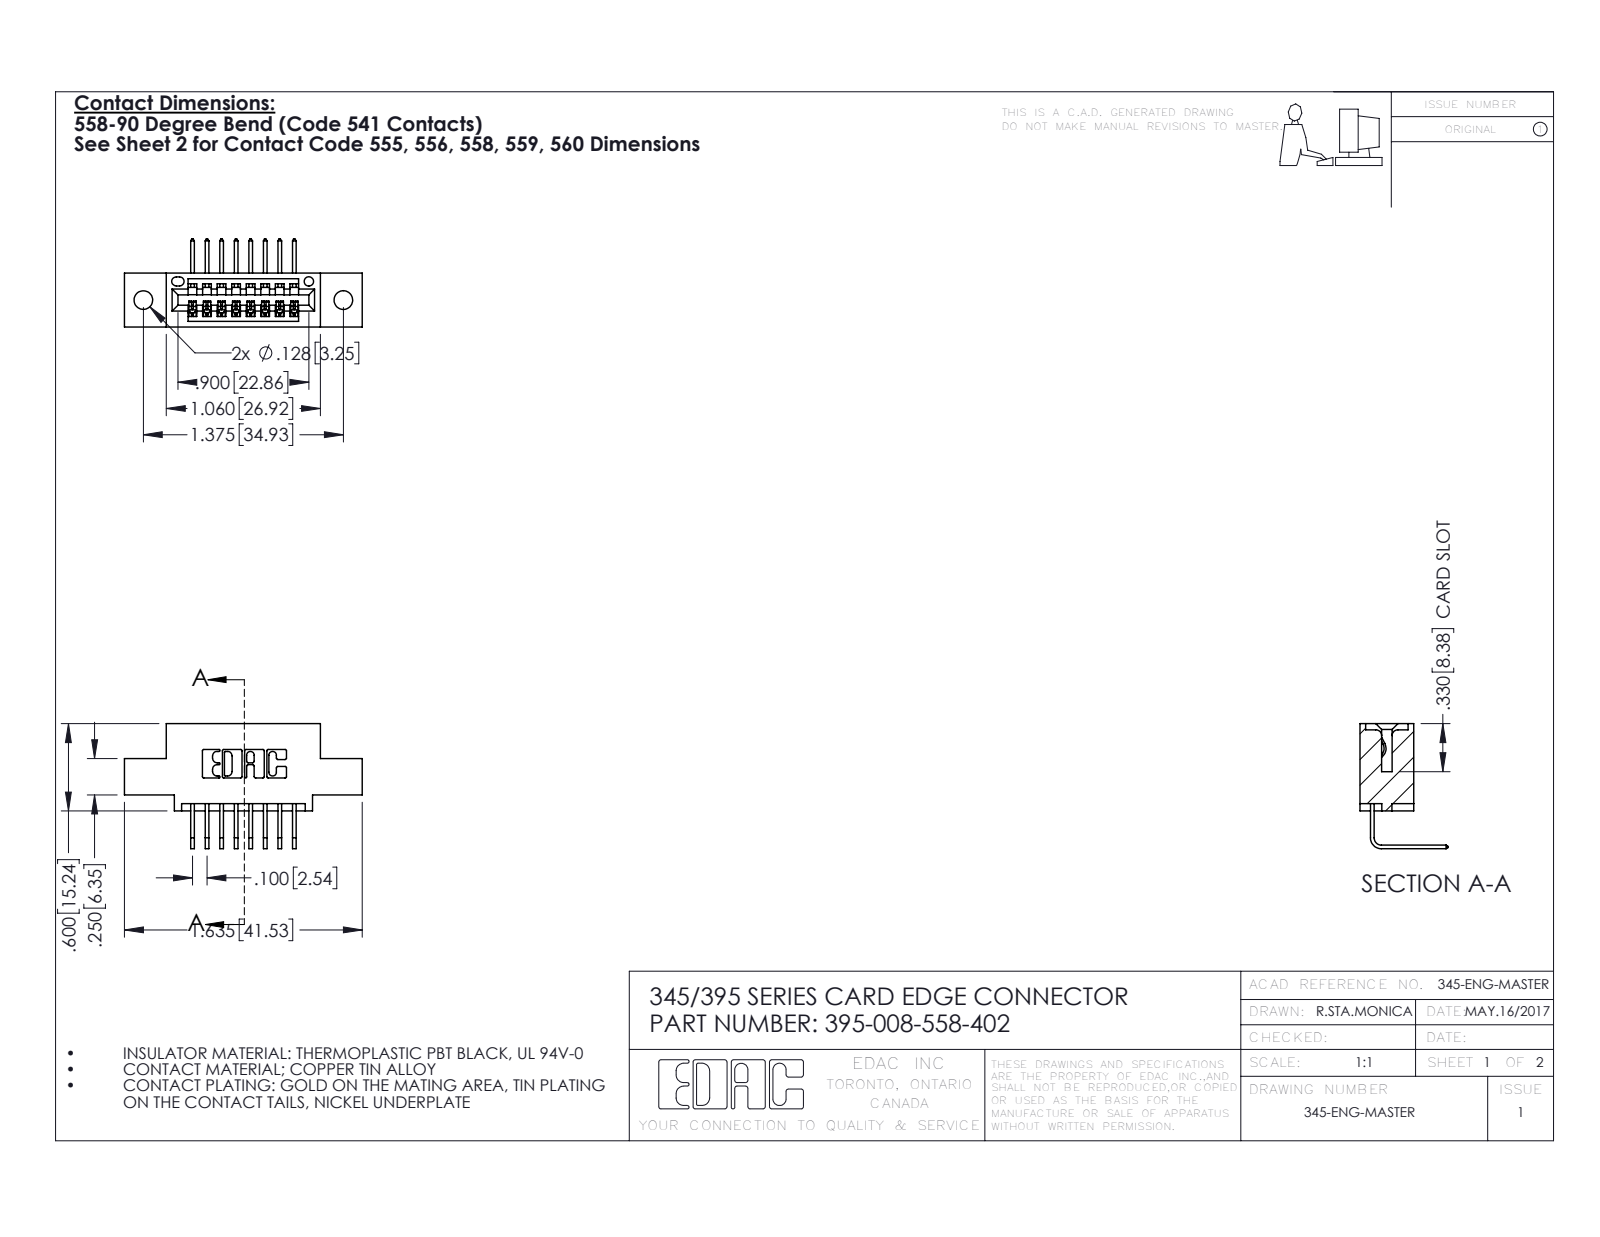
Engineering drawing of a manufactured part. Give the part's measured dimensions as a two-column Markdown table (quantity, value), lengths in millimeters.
| quantity | value |
| --- | --- |
| part name | 345-292-001_558 Tail - 2; 395-008-558-402; 345 Part_0.110 Offset - 0.128 Dia |
| STEP written by | SolidWorks 2016 (CONFIG_CONTROL_DESIGN) |
| units | millimeters |
| bodies | 9 solids, 610 faces (420 planar, 190 cylindrical, 0 other) |
| overall size | 41.5 × 21.8 × 15.4 |
| volume | 3 590 mm³ |
| surface area | 4 266 mm² |
| round holes (diameter × count) | 3.3 × 2, 1.6 × 1 |
| partial cylindrical surfaces (radius × count) | 0.3 × 22, 0.2 × 16, 0.2 × 6, 0.8 × 6, 0.7 × 3, 0.8 × 2, 1 × 2, 0.4 × 1 |
| main face-to-face distances | 5.1, 9.4, 2.5, 1.8, 7.6, 7.6, 4.1, 2.5, 6.9, 0.6 |
| hole center spacings | 6.9, 29.1, 34.9 |
